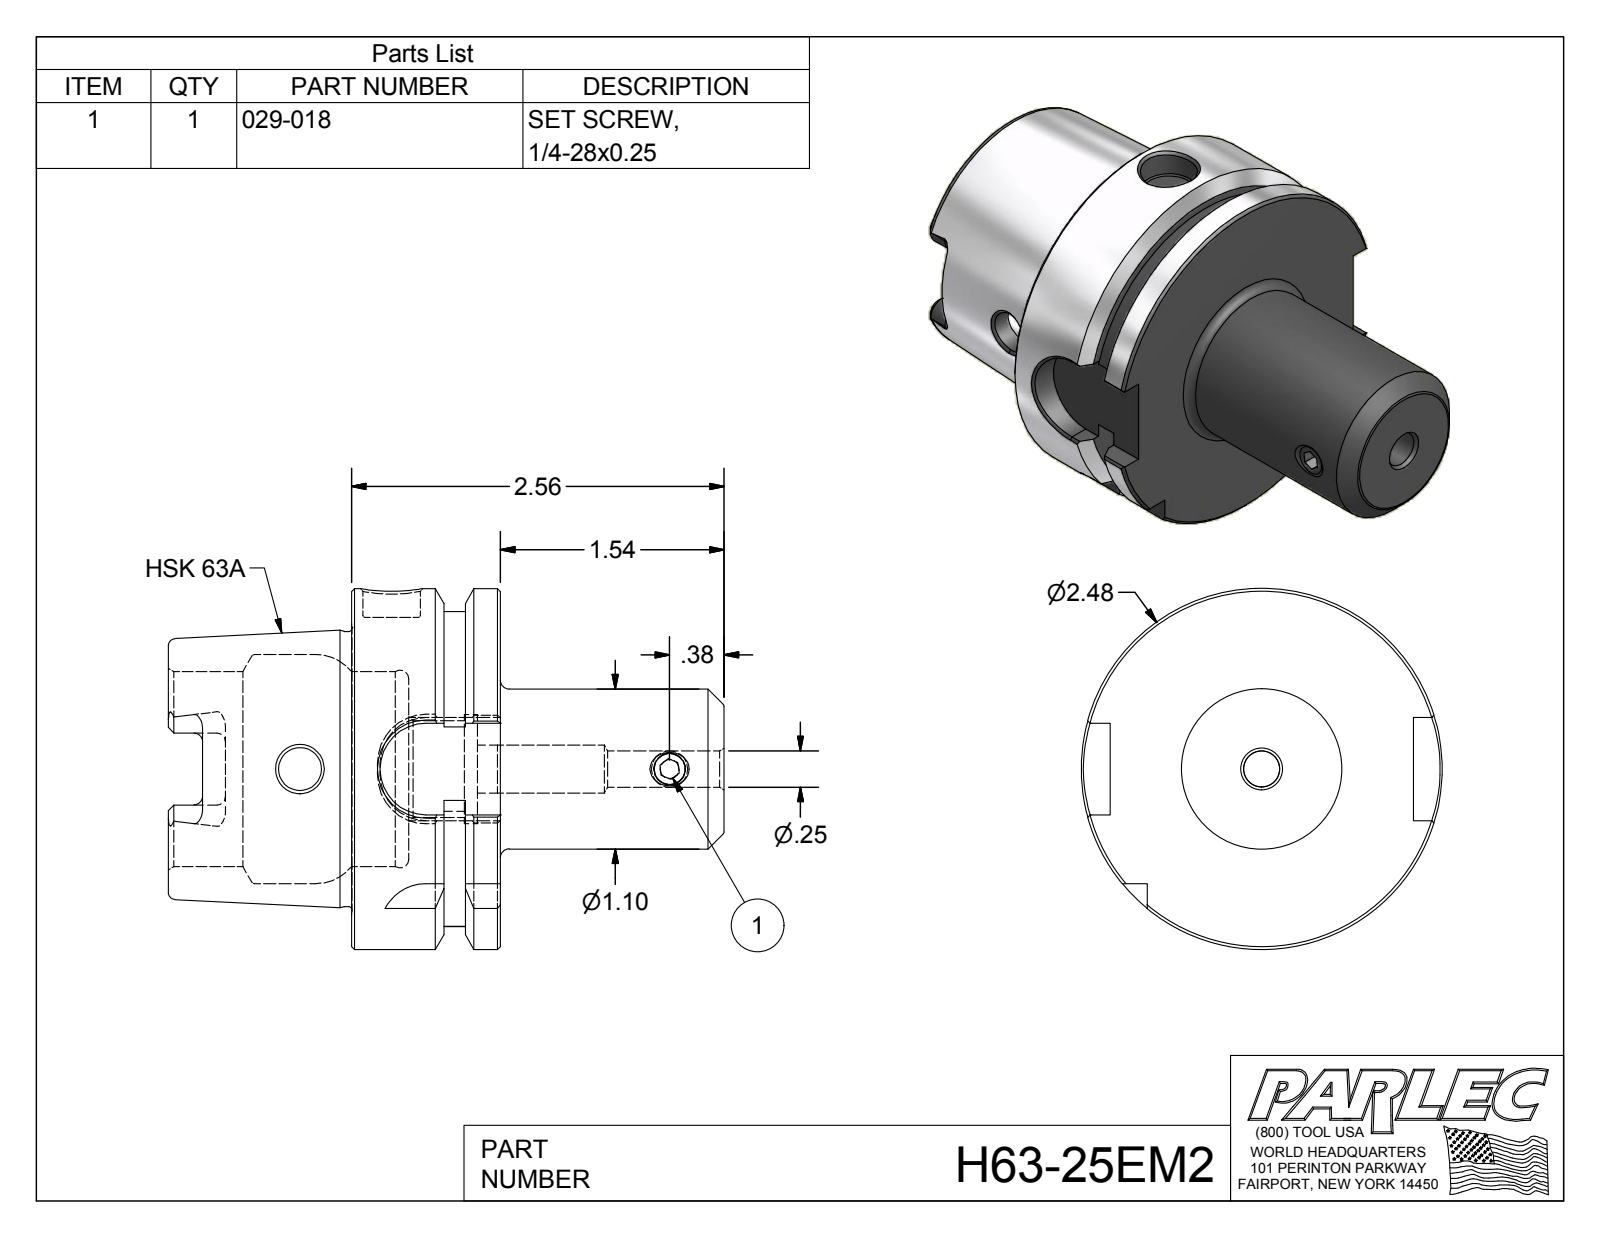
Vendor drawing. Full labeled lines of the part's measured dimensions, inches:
Part name (STEP PRODUCT): H63-25EM2; H63-25EM2-1; 029-018
STEP written by: Autodesk Inventor 2012 (AUTOMOTIVE_DESIGN)
Units: inches
Bodies: 2 solids, 151 faces (62 planar, 37 cylindrical, 52 other)
Overall size (bounding box): 3.822 × 2.48 × 2.48
Volume: 6.283 in³ · Surface area: 41.84 in²
Round holes (diameter × count): ⌀0.211 ×1, ⌀0.25 ×1, ⌀0.295 ×1, ⌀0.33 ×1, ⌀0.331 ×1, ⌀0.394 ×1, ⌀0.666 ×1, ⌀0.749 ×1, ⌀1.339 ×1, ⌀1.575 ×1
Round bosses / shafts (diameter × count): ⌀2.48 ×1, ⌀1.891 ×1, ⌀1.1 ×1, ⌀0.25 ×1
Partial cylindrical surfaces — rounded edges, fillets, slot ends (radius × count): R0.059 ×6, R0.113 ×4, R0.315 ×4, R1.083 ×1
Main face-to-face distances: 1.024, 0.241, 0.389, 0.394, 0.63, 1.26, 1.654, 2.283, 3.822, 2.562
Hole centre spacings: 2.541
